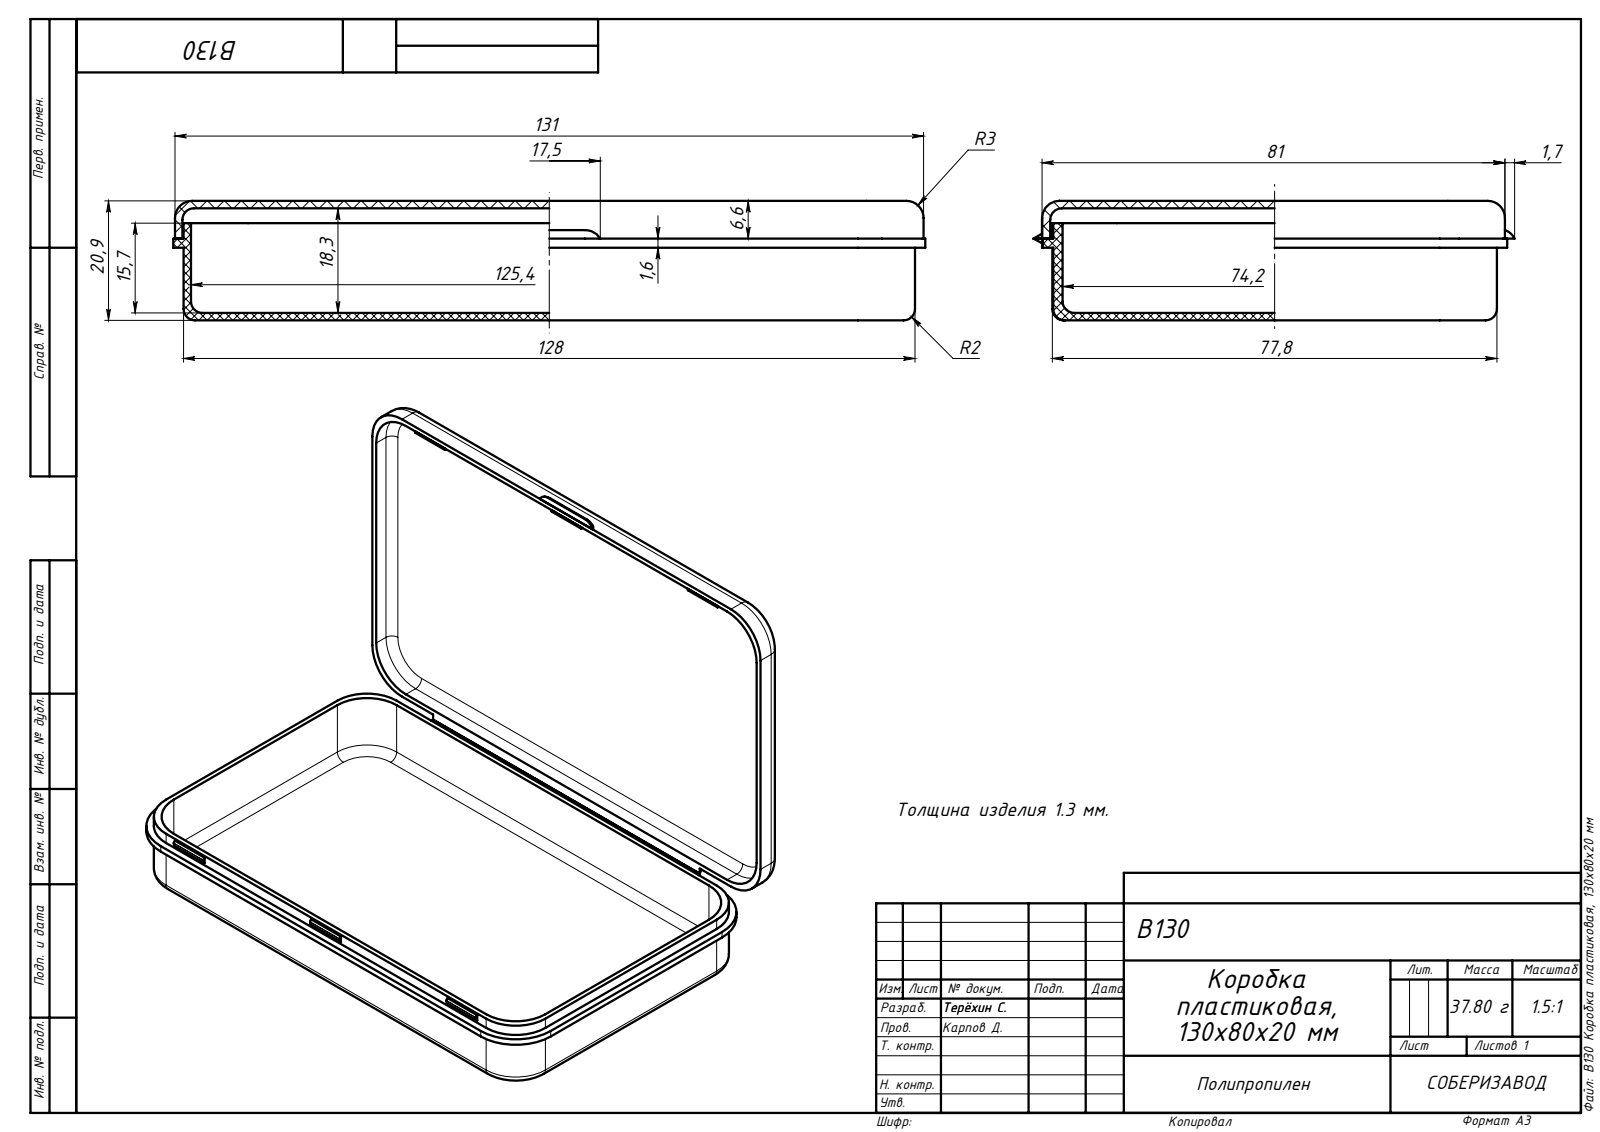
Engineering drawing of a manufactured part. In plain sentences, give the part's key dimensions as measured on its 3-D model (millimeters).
The part is named "B130 Крышка_00; B130 Емкость_00; B130 Коробка пластиковая, 130x80x20 мм". Its 3-D file was written by "SolidWorks 2019 (AUTOMOTIVE_DESIGN)". It is 6 solids with 129 faces: 61 planar, 44 cylindrical and 24 other. Overall it measures 131.6 by 84.2 by 20.9 millimeters. Its volume is 38 562 cubic millimeters and its surface area 58 858 square millimeters. Partial cylindrical surfaces (rounded edges, fillets, slot ends): 16 of radius 10, 12 of radius 2, 5 of radius 3, 4 of radius 11.8, 1 of radius 0.5. The main face-to-face distances are 1.3, 19.6, 20.9, 18.3, 76.5, 13, 14.3, 5.3, 6.6, 126.7.
